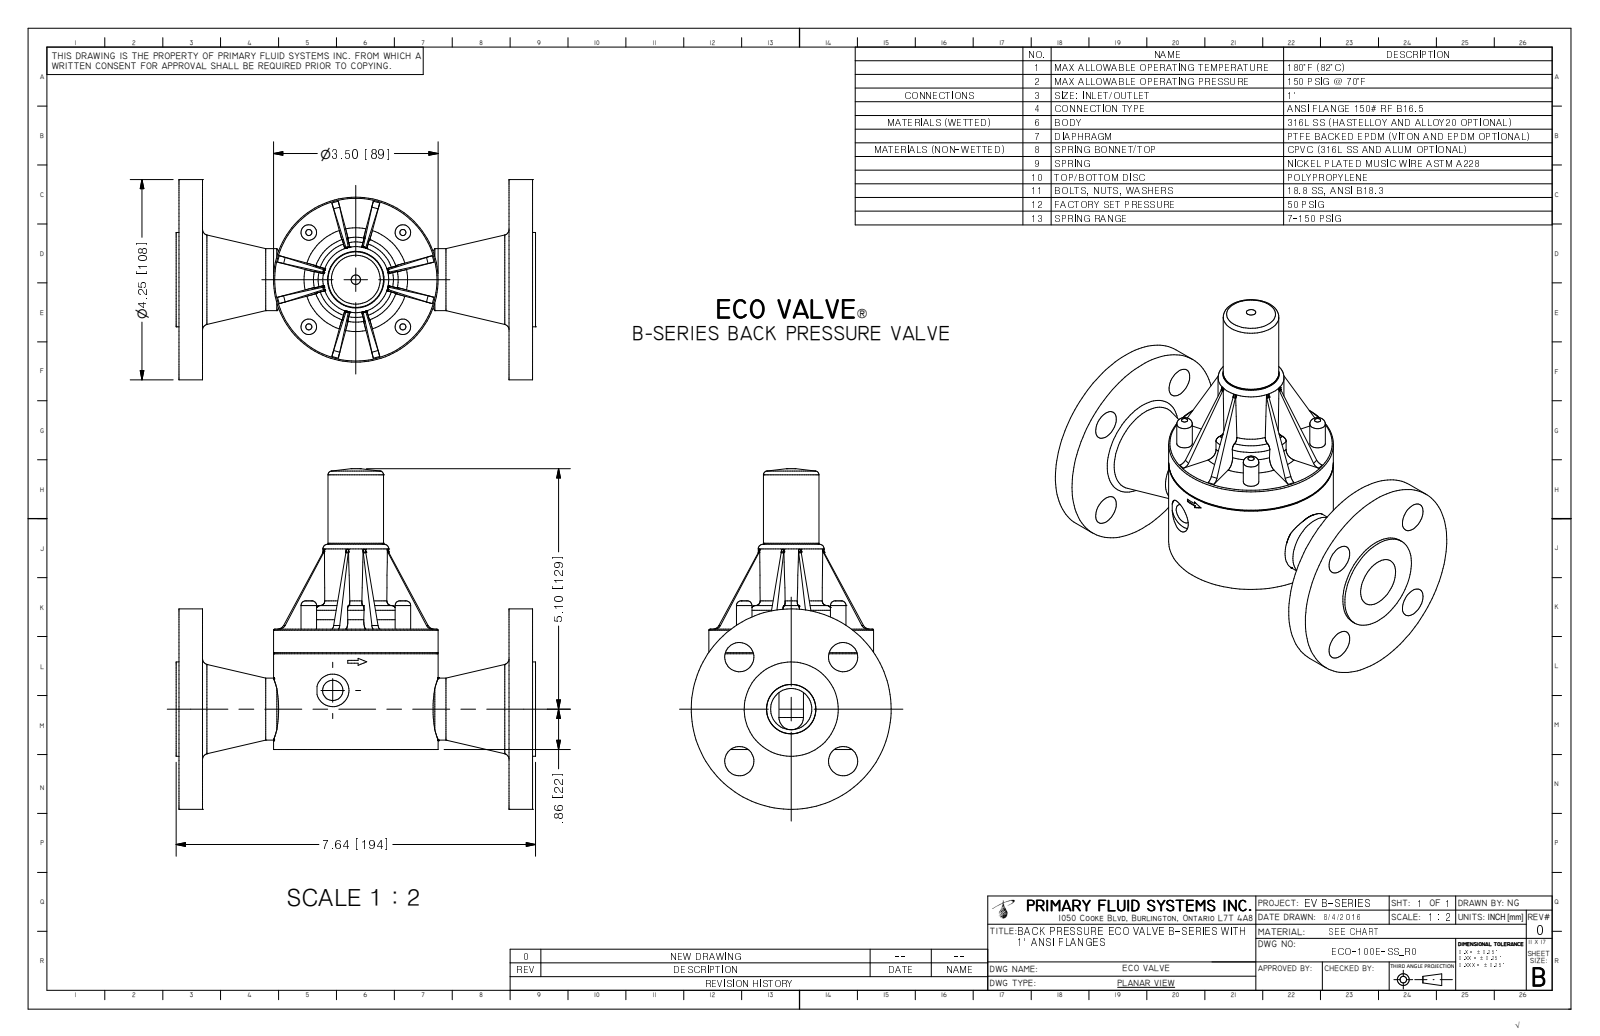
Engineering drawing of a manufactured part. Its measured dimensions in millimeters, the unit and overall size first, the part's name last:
Units: millimetres
Overall size (bounding box): 194.1 × 183.4 × 108
Round holes (diameter × count): ⌀15.7 ×4, ⌀10.9 ×1, ⌀17.6 ×1, ⌀26.6 ×1
Round bosses / shafts (diameter × count): ⌀8.4 ×4, ⌀108 ×1, ⌀88.9 ×1, ⌀50.8 ×1, ⌀45.7 ×1, ⌀35.6 ×1, ⌀33.4 ×1, ⌀30 ×1
Partial cylindrical surfaces — rounded edges, fillets, slot ends (radius × count): R3.8 ×8, R43.9 ×1
Main face-to-face distances: 12.7, 178.2, 190.9, 165.5, 1.6, 14.3, 179.8, 192.5, 64.9, 194.1
Hole centre spacings: 39.6, 56, 79.2
Volume: 752 700 mm³ · Surface area: 109 700 mm²
Bodies: 1 solid, 180 faces (64 planar, 45 cylindrical, 71 other)
Part name (STEP PRODUCT): ECO-100E-SS_R0
STEP written by: Autodesk Inventor 2009 (AUTOMOTIVE_DESIGN)
